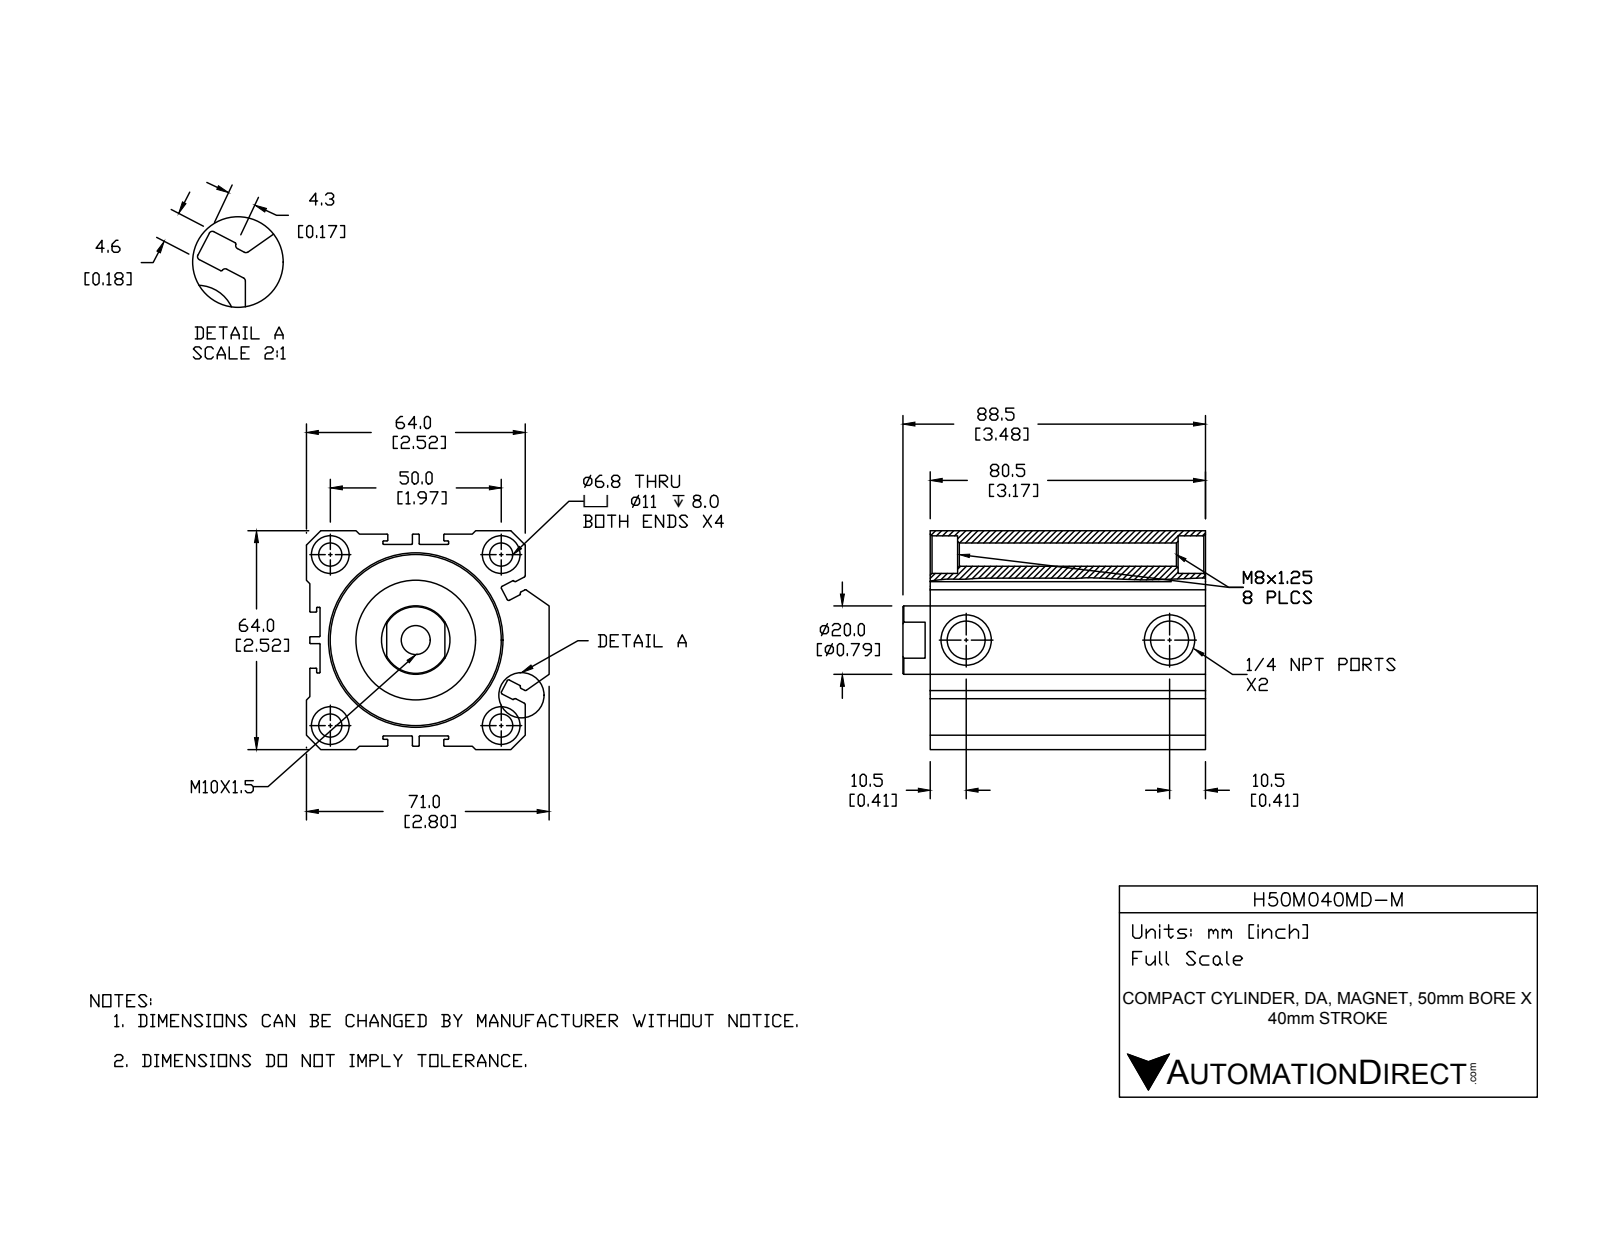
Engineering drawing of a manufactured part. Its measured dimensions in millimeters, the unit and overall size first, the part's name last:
Units: millimetres
Overall size (bounding box): 88.5 × 71 × 64
Round holes (diameter × count): ⌀6.8 ×4, ⌀11 ×4, ⌀11.13 ×2, ⌀8.5 ×1, ⌀20 ×1, ⌀36 ×1, ⌀50 ×1
Round bosses / shafts (diameter × count): ⌀35 ×1, ⌀31 ×1
Partial cylindrical surfaces — rounded edges, fillets, slot ends (radius × count): R0.2 ×40, R0.5 ×12
Main face-to-face distances: 4, 1, 3, 63, 60, 64, 7, 30, 70, 59
Hole centre spacings: 35.36, 50, 70.71, 59.5
Volume: 222 035 mm³ · Surface area: 69 662 mm²
Bodies: 2 solids, 255 faces (99 planar, 103 cylindrical, 53 other)
Part name (STEP PRODUCT): H50M040MD-M-BODY; H50M040MD-M-PISTON; H50M040MD-M
STEP written by: SolidWorks 2015 (CONFIG_CONTROL_DESIGN)
